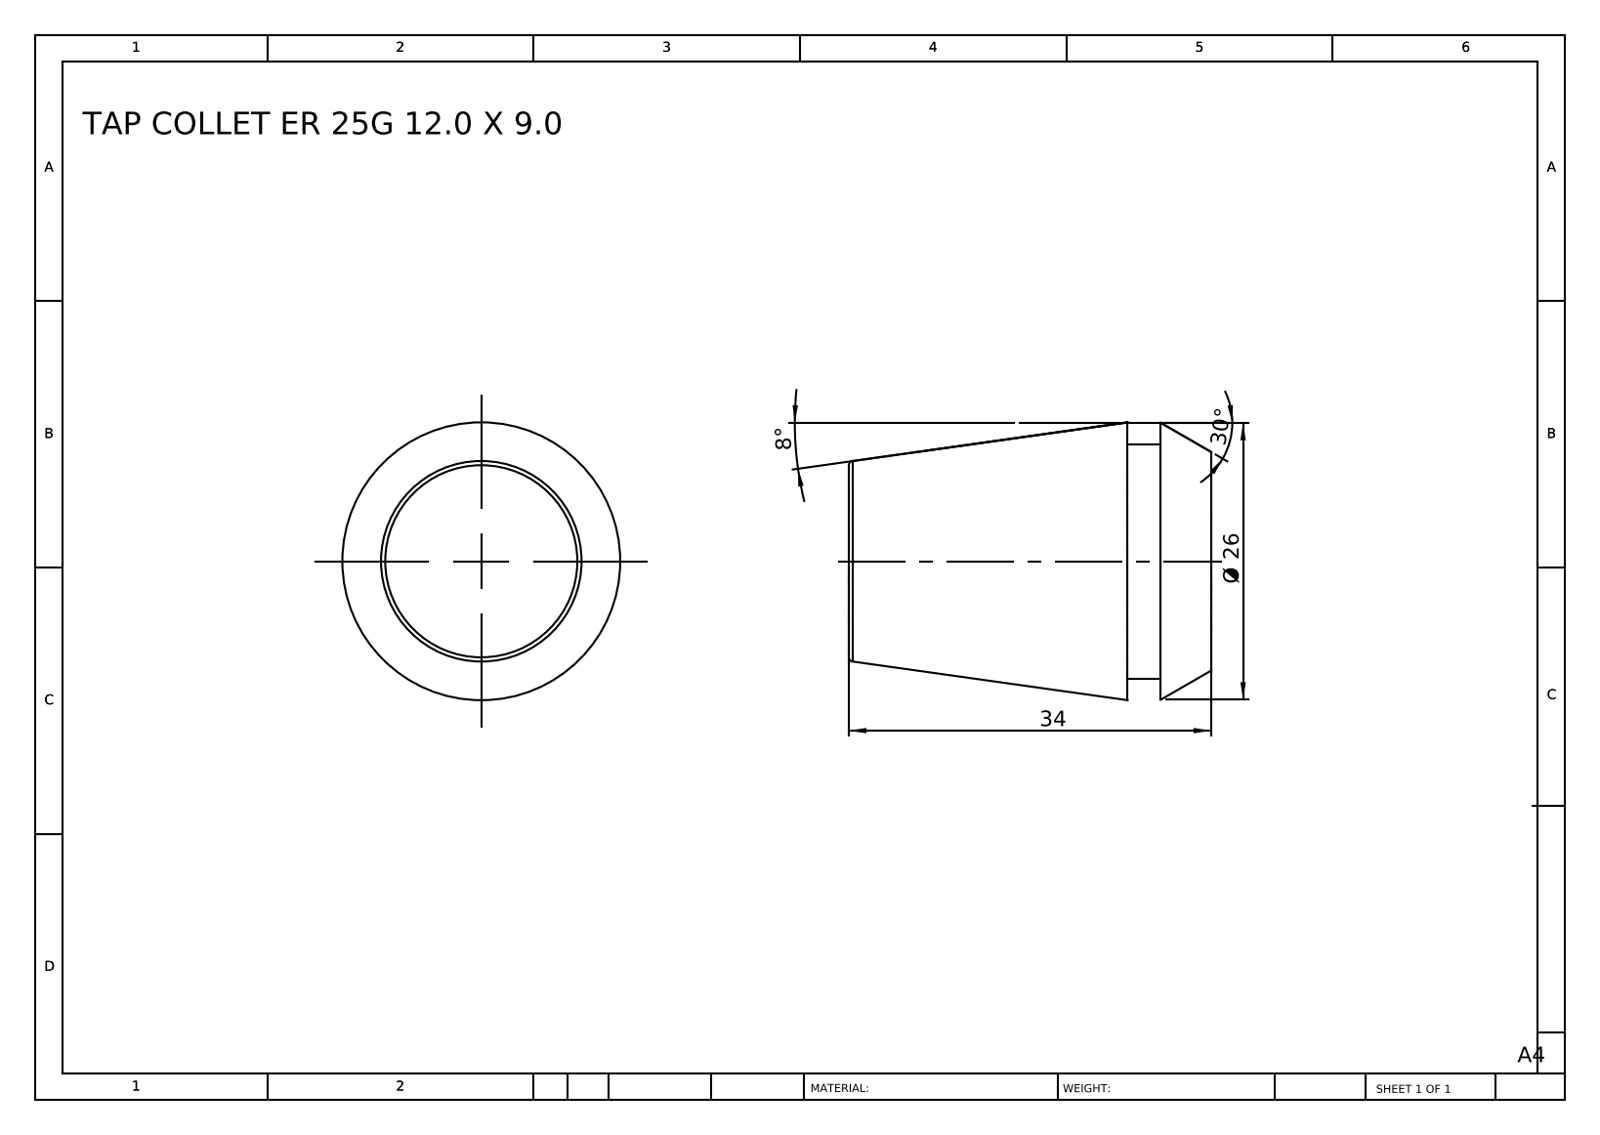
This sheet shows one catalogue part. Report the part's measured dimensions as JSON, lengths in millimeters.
{"part_name": "TAP COLLET ER 25G 12.0 X 9.0", "step_written_by": "SolidWorks 2014 (CONFIG_CONTROL_DESIGN)", "units": "millimeters", "bodies": {"solids": 1, "faces": 12, "planar": 4, "cylindrical": 2, "other": 6}, "overall_size": [34, 26.07, 26.07], "volume_mm3": 13600, "surface_area_mm2": 3376, "round_bosses_or_shafts": [[22, 1]], "face_to_face_distances": [34, 7.84, 26.16, 4.74, 3.1, 29.26]}
